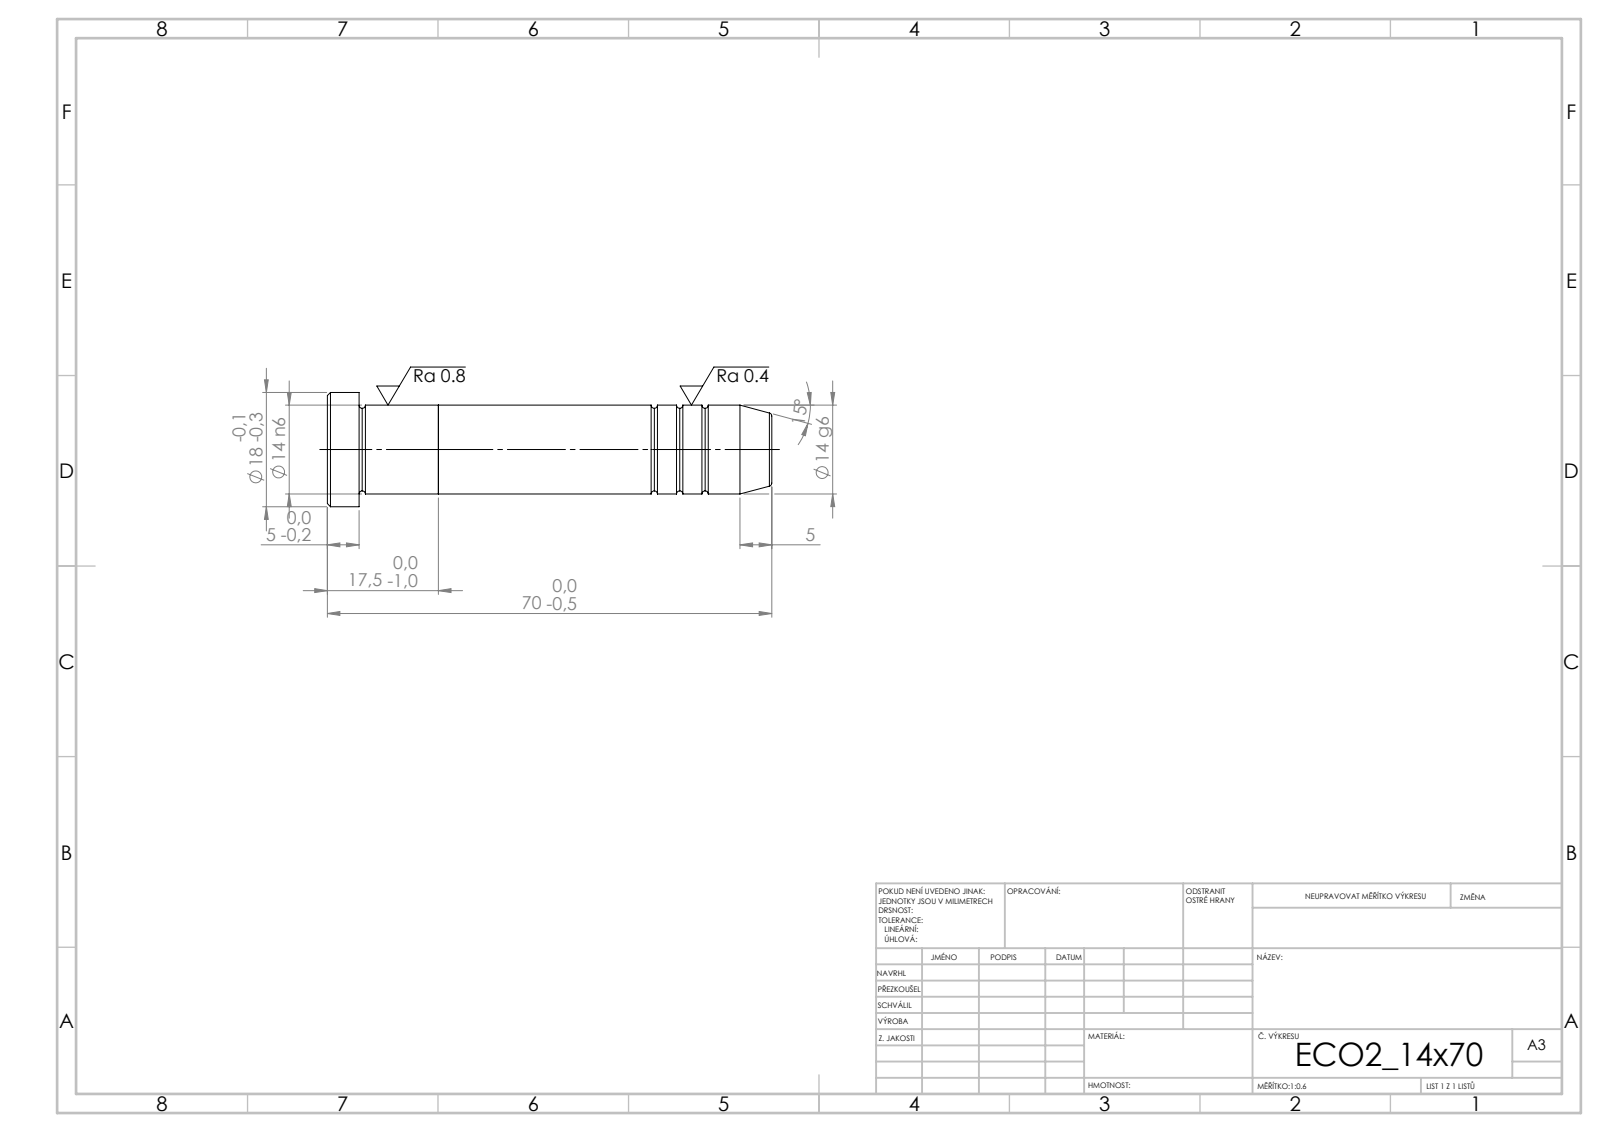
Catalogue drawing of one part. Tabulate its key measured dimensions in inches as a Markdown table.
| quantity | value |
| --- | --- |
| STEP written by | SolidWorks 2019 (CONFIG_CONTROL_DESIGN) |
| units | inches |
| bodies | 2 solids, 39 faces (5 planar, 12 cylindrical, 22 other) |
| overall size | 2.756 × 0.709 × 0.709 |
| volume | 0.675 in³ |
| surface area | 6.135 in² |
| round bosses / shafts (diameter × count) | 0.709 × 1, 0.551 × 1 |
| main face-to-face distances | 0.689, 0.492, 0.197, 2.067, 2.559, 2.756 |
